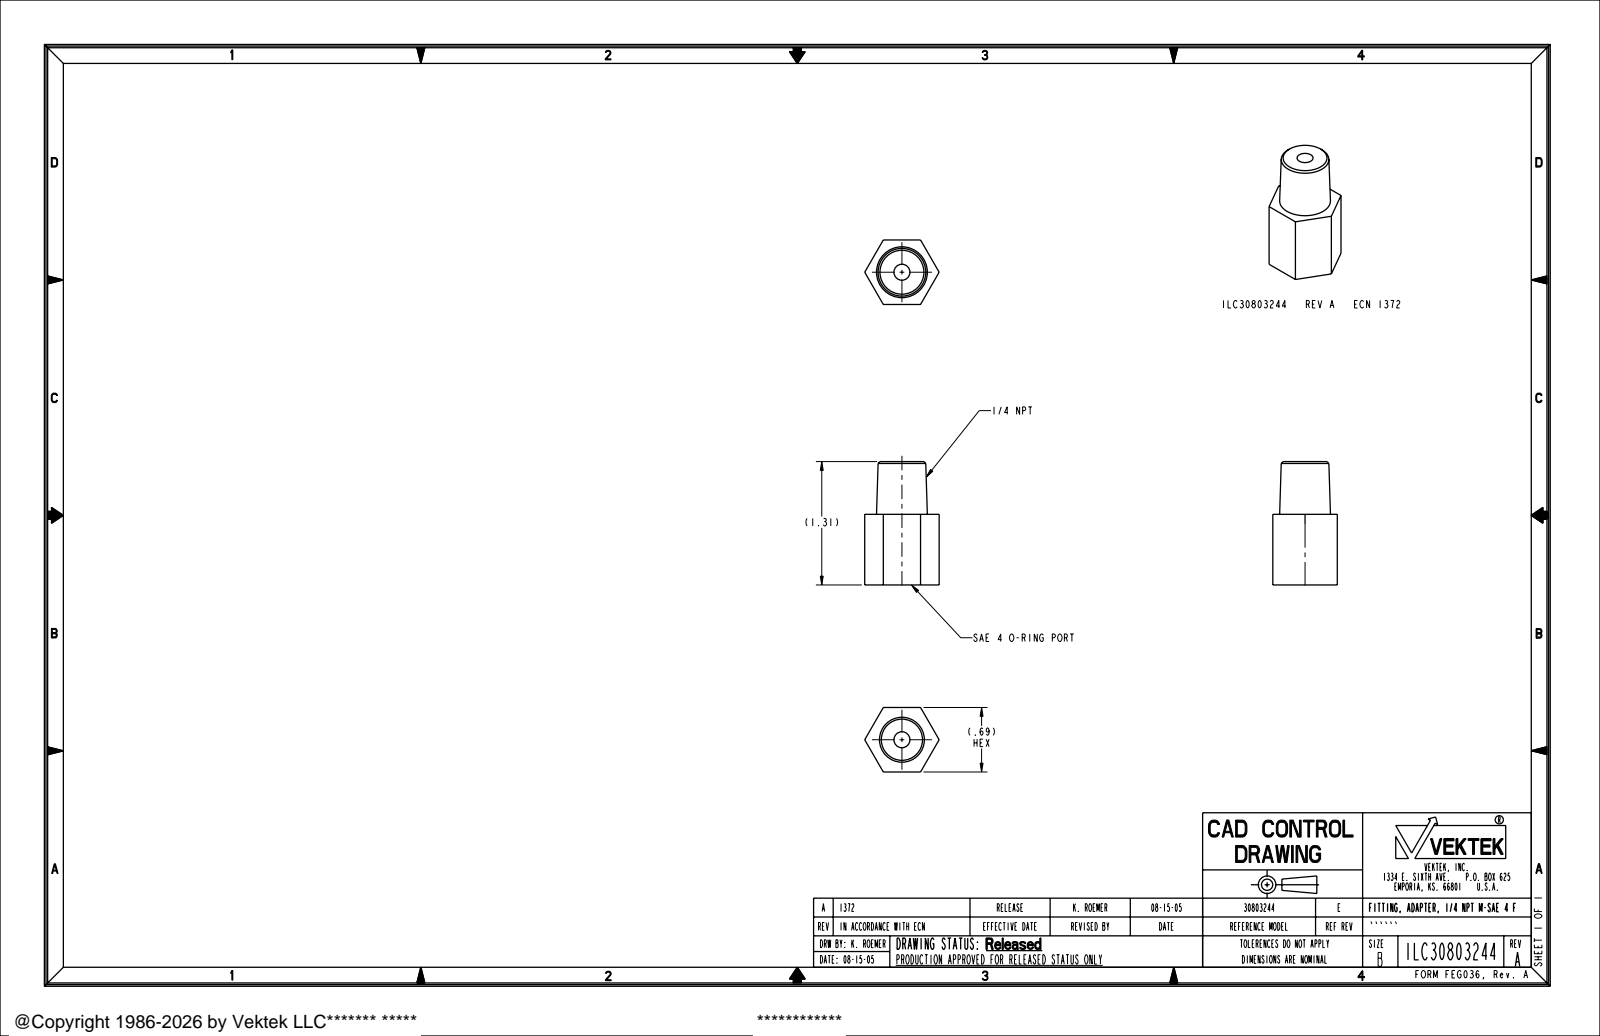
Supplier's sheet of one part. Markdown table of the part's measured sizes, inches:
| quantity | value |
| --- | --- |
| part name | ILC30803244 |
| STEP written by | PRO/ENGINEER BY PARAMETRIC TECHNOLOGY CORPORATION, 2004290 (AUTOMOTIVE_DESIGN_CC2) |
| units | inches |
| bodies | 1 solid, 20 faces (10 planar, 4 cylindrical, 6 other) |
| overall size | 1.31 × 0.791 × 0.685 |
| volume | 0.324 in³ |
| surface area | 4.56 in² |
| round holes (diameter × count) | 0.17 × 1, 0.437 × 1 |
| main face-to-face distances | 0.685, 0.75, 1.31, 0.56, 0.547, 0.203, 0.763 |
